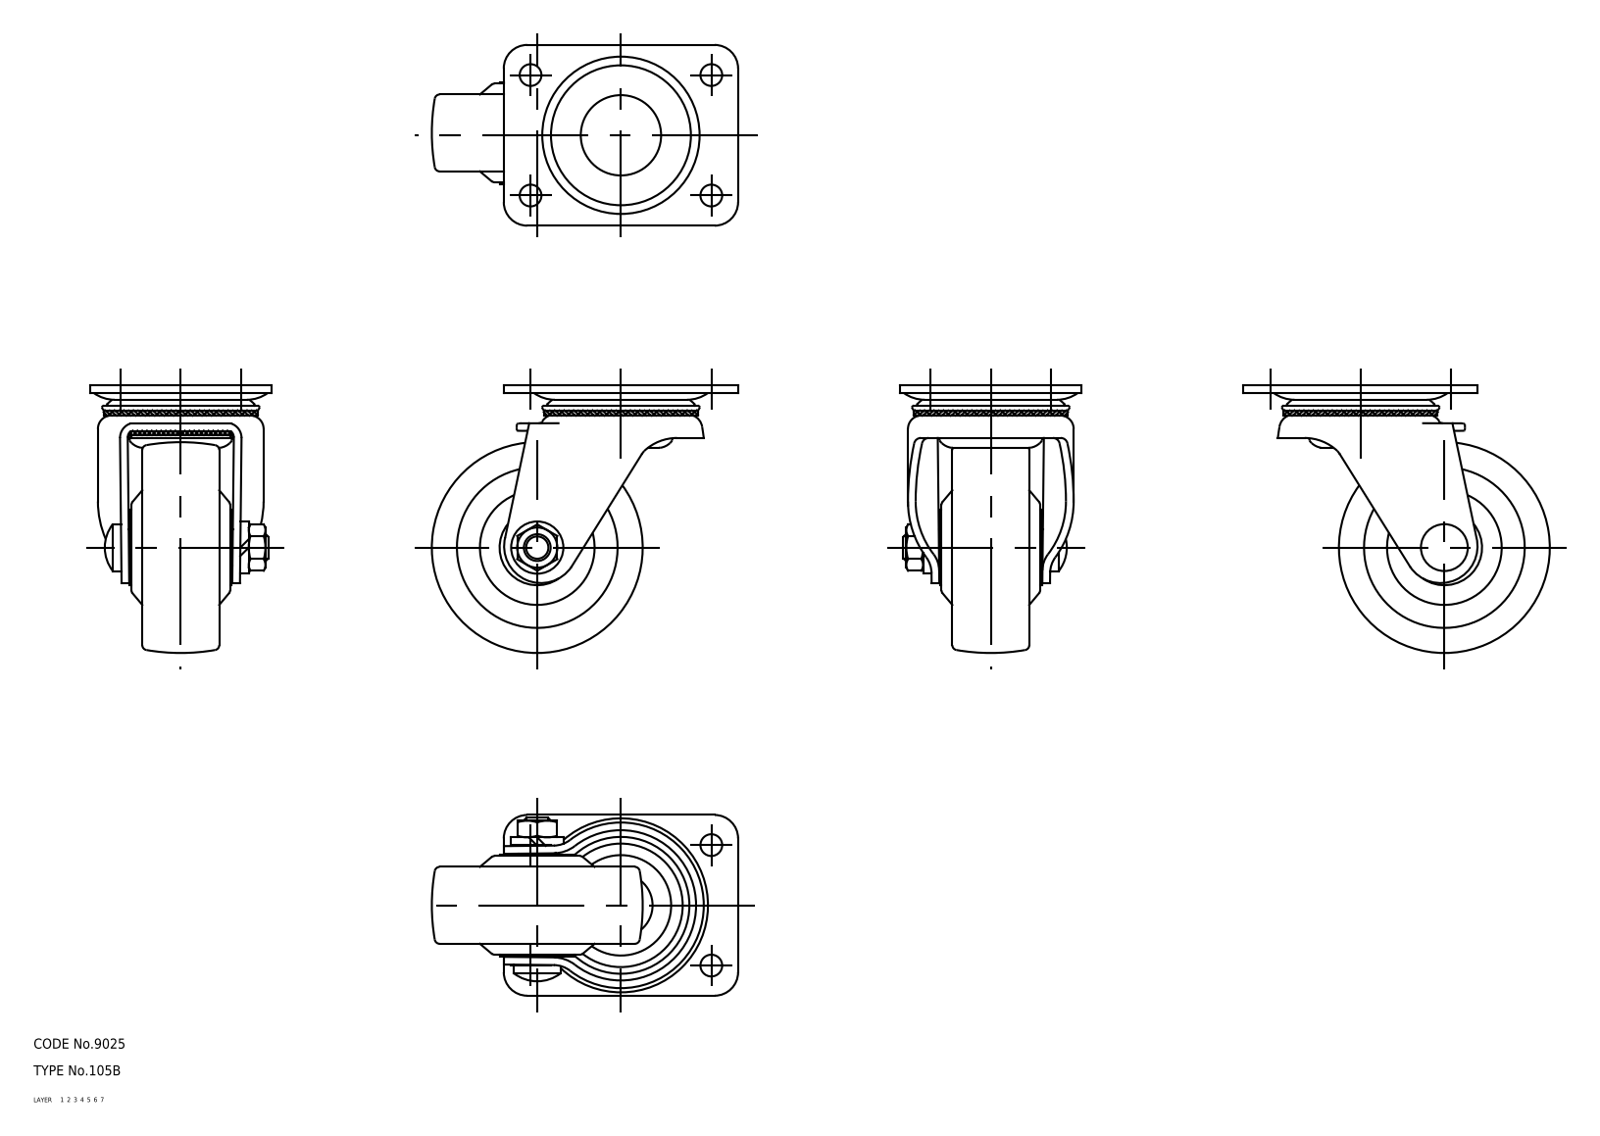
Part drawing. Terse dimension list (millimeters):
name: 67128650; 67128663; 67128676; 67128689 (+8 more)
written by: CADfix (AUTOMOTIVE_DESIGN)
unit: mm
bodies: 4 solids, 258 faces (0 planar, 0 cylindrical, 258 other)
size: 91.5 × 80 × 54
volume: 99 389 mm³; area: 38 103 mm²
